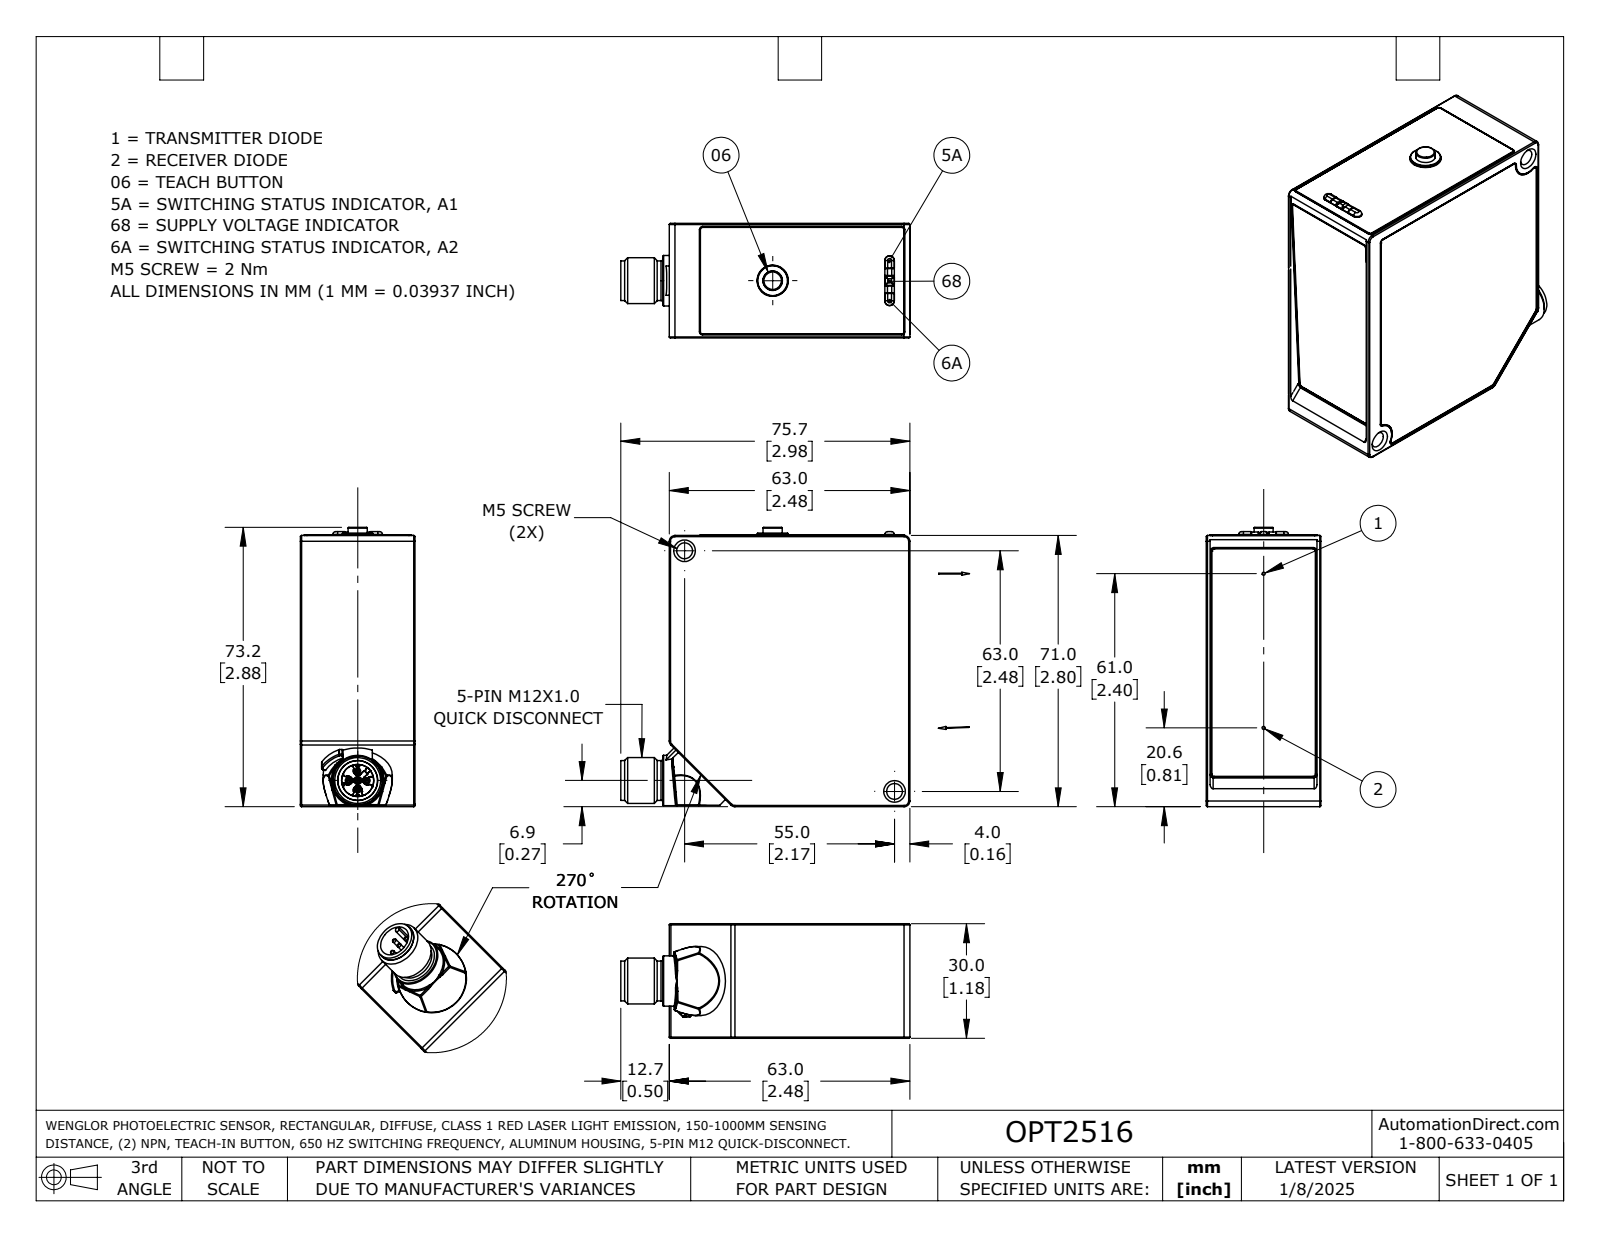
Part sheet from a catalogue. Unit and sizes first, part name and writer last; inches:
Units: inches
Overall size (bounding box): 3.594 × 2.88 × 1.181
Round holes (diameter × count): ⌀0.06 ×5, ⌀0.163 ×2, ⌀0.201 ×1
Round bosses / shafts (diameter × count): ⌀0.039 ×5, ⌀0.064 ×3, ⌀0.008 ×2, ⌀0.713 ×1, ⌀0.52 ×1, ⌀0.472 ×1, ⌀0.409 ×1, ⌀0.315 ×1
Partial cylindrical surfaces — rounded edges, fillets, slot ends (radius × count): R0.012 ×28, R0.026 ×11, R0.028 ×6, R0.03 ×6, R0.059 ×6, R0.004 ×4, R0.027 ×4, R0.032 ×4
Main face-to-face distances: 1.178, 2.799, 1.181, 2.795, 0.039, 1.142, 2.48, 2.785, 2.789, 1.102
Hole centre spacings: 0.098, 0.139, 0.197, 3.293
Volume: 7.872 in³ · Surface area: 28.96 in²
Bodies: 3 solids, 390 faces (163 planar, 115 cylindrical, 112 other)
Part name (STEP PRODUCT): OPT2515_OPT2516
STEP written by: SolidWorks 2024 (AUTOMOTIVE_DESIGN)
